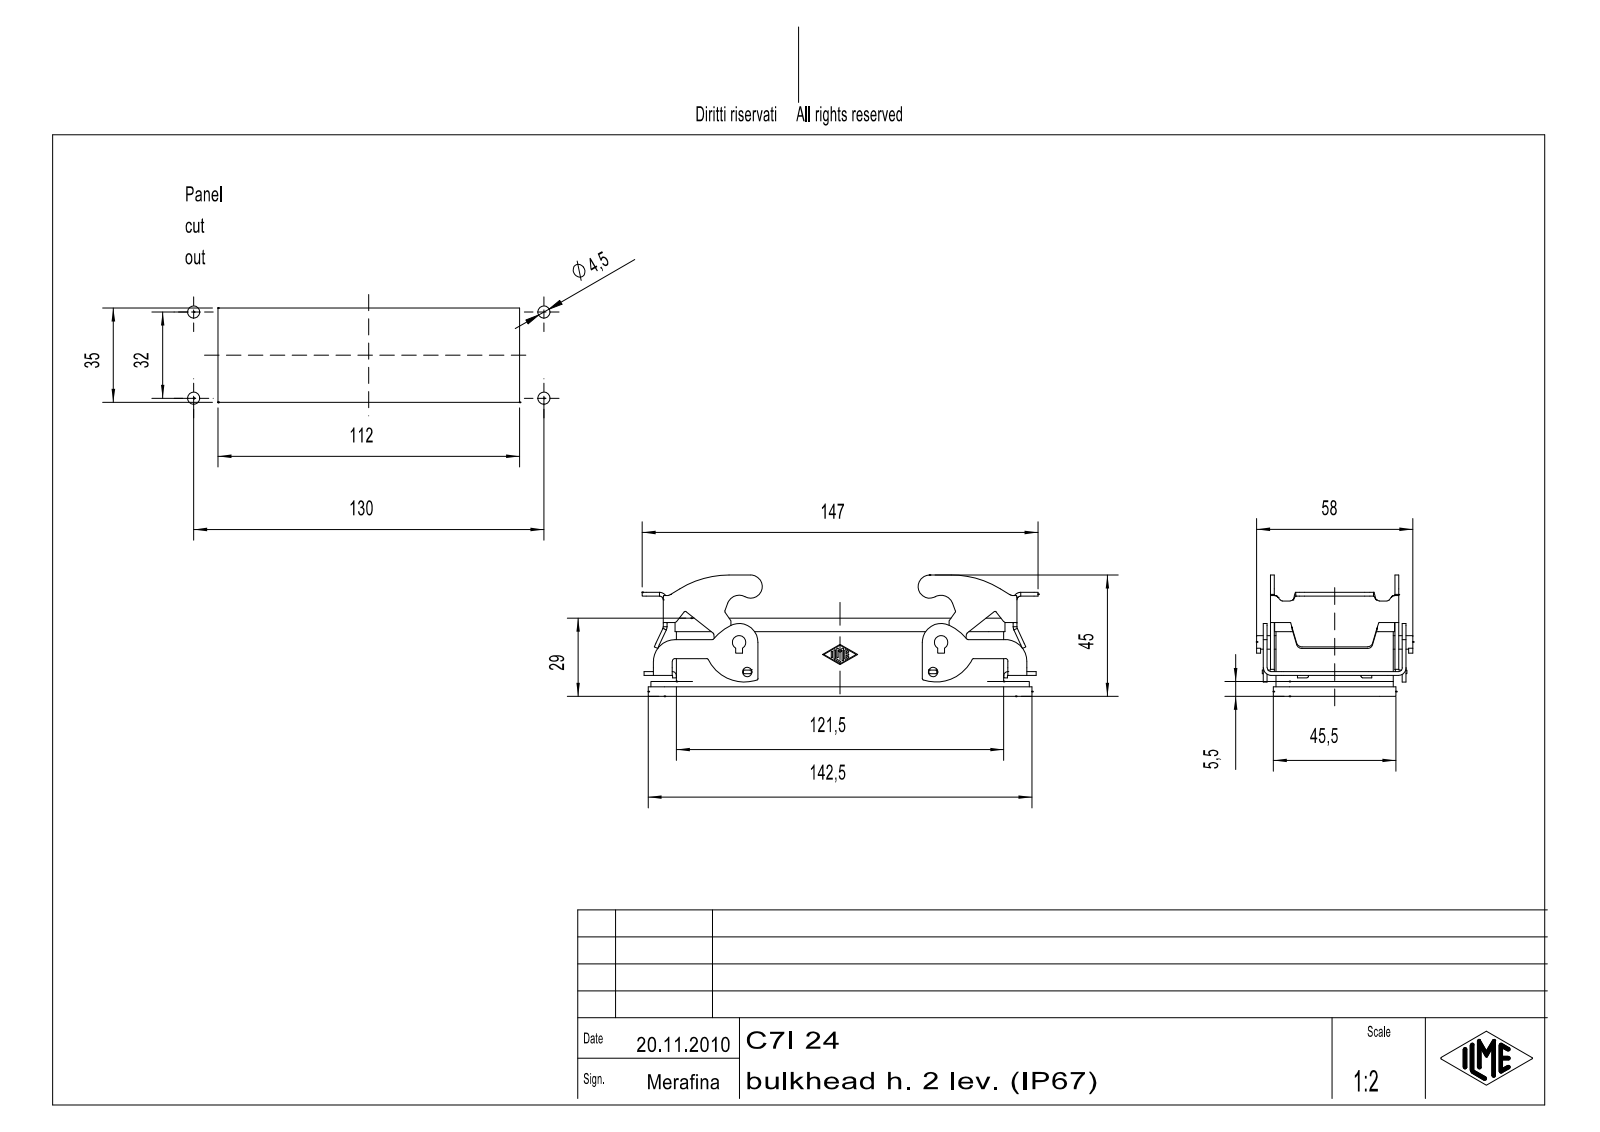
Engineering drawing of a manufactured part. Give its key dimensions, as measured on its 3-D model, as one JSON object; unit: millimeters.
{"part_name": "CVI 24", "step_written_by": "Autodesk Inventor 7 (AUTOMOTIVE_DESIGN)", "units": "millimeters", "bodies": {"solids": 3, "faces": 601, "planar": 199, "cylindrical": 182, "other": 220}, "overall_size": [146.97, 58, 45], "volume_mm3": 47674, "surface_area_mm2": 41403, "round_holes": [[4.5, 4], [3.5, 2]], "round_bosses_or_shafts": [[5, 2]], "partial_cylinders_radius": [[0.5, 18], [0.25, 16], [1, 14], [1.5, 12], [3, 12], [6, 12], [1.4, 10], [2.8, 10]], "face_to_face_distances": [40.5, 3, 0.5, 3.5, 1.4, 4, 43.5, 37.5, 41, 1], "hole_center_spacings": [32, 130, 133.88, 69]}
